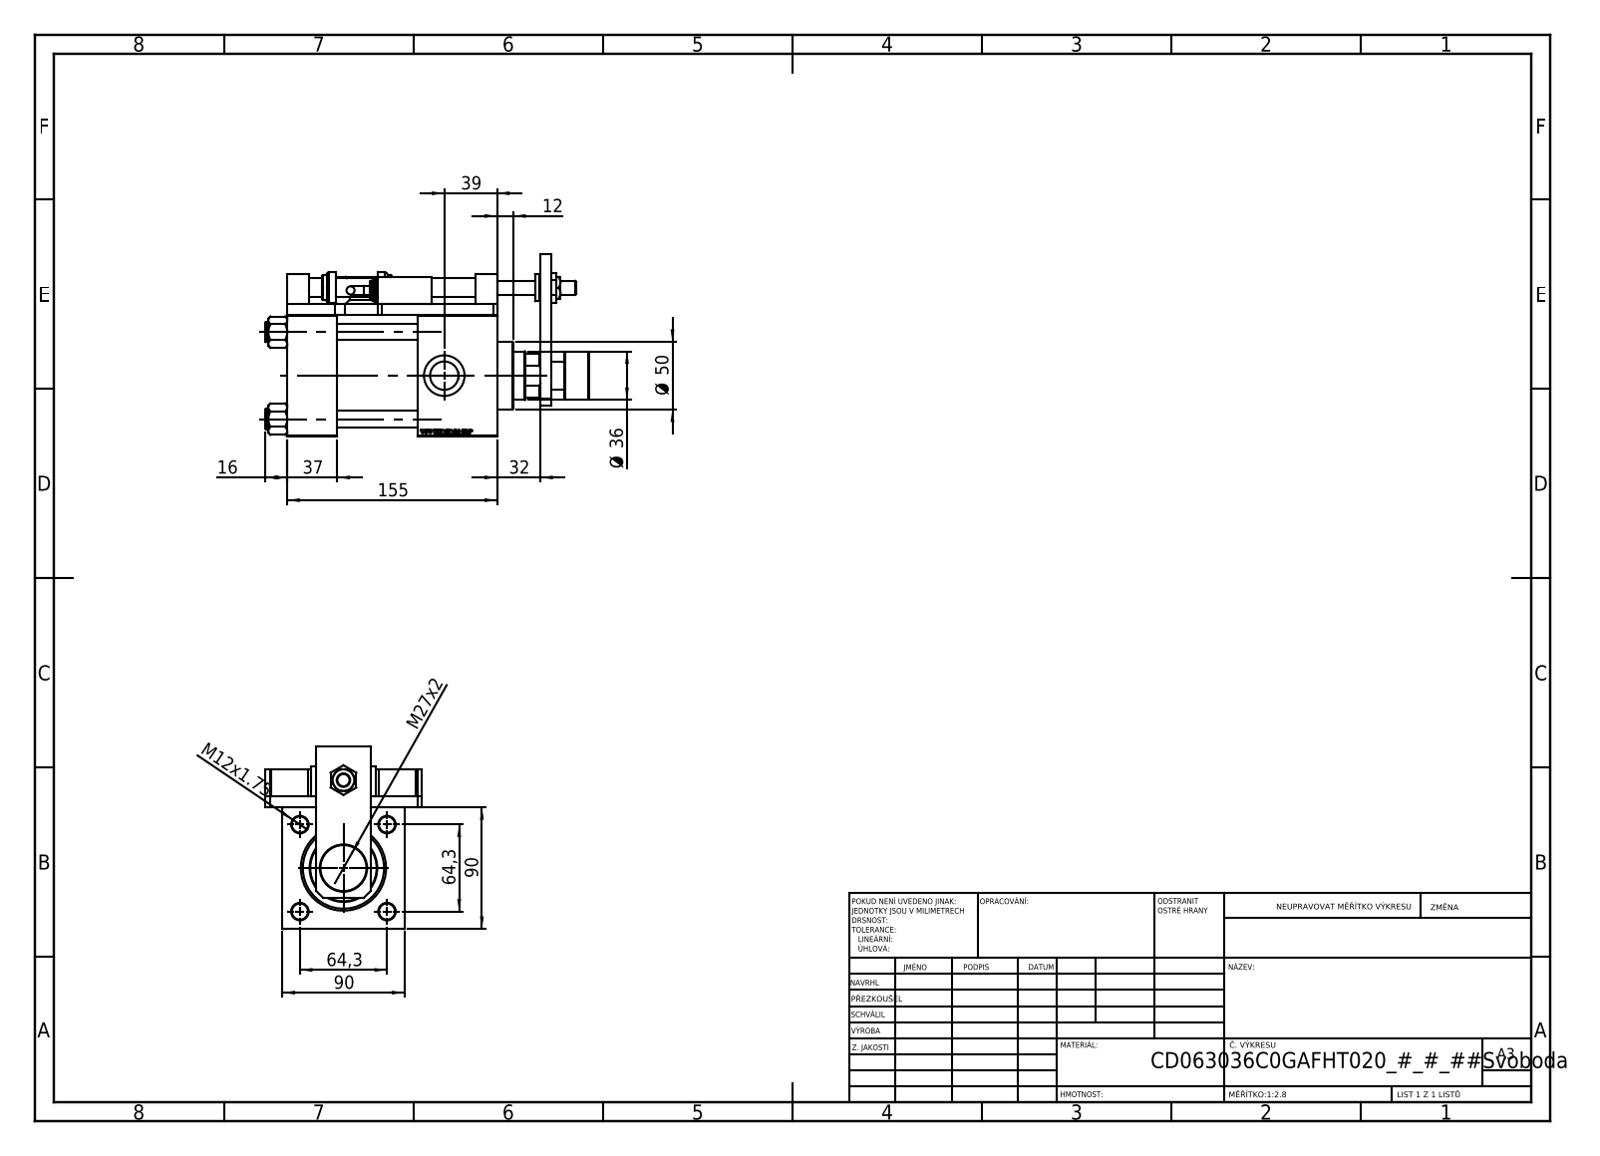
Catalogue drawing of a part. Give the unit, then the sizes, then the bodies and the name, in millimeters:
Units: millimetres
Overall size (bounding box): 239 × 135 × 115
Round holes (diameter × count): ⌀8.5 ×4, ⌀12 ×4, ⌀13.5 ×4, ⌀7 ×2, ⌀20.96 ×2, ⌀30 ×2, ⌀10 ×1, ⌀14 ×1, ⌀25.5 ×1, ⌀27 ×1, ⌀36 ×1, ⌀39 ×1
Round bosses / shafts (diameter × count): ⌀15 ×4, ⌀20 ×3, ⌀16 ×2, ⌀14 ×2, ⌀6 ×2, ⌀69 ×1, ⌀35 ×1, ⌀23 ×1
Partial cylindrical surfaces — rounded edges, fillets, slot ends (radius × count): R7.5 ×4
Main face-to-face distances: 8, 90, 37, 59, 118, 98, 155, 20, 32, 91
Hole centre spacings: 45.47, 64.3, 19.14, 32, 45.96, 90.93, 102.33, 129.49
Volume: 1 255 000 mm³ · Surface area: 274 705 mm²
Bodies: 25 solids, 1391 faces (651 planar, 159 cylindrical, 581 other)
Part name (STEP PRODUCT): V215CD_SWITCH_Q_PODLOZKA_FRONT; V215CD_SWITCH_Q_DIMA; V215CD_Body_C; V215CD_SWITCH_Q_ZARAZKA (+7 more)
STEP written by: SolidWorks 2019 (CONFIG_CONTROL_DESIGN)
